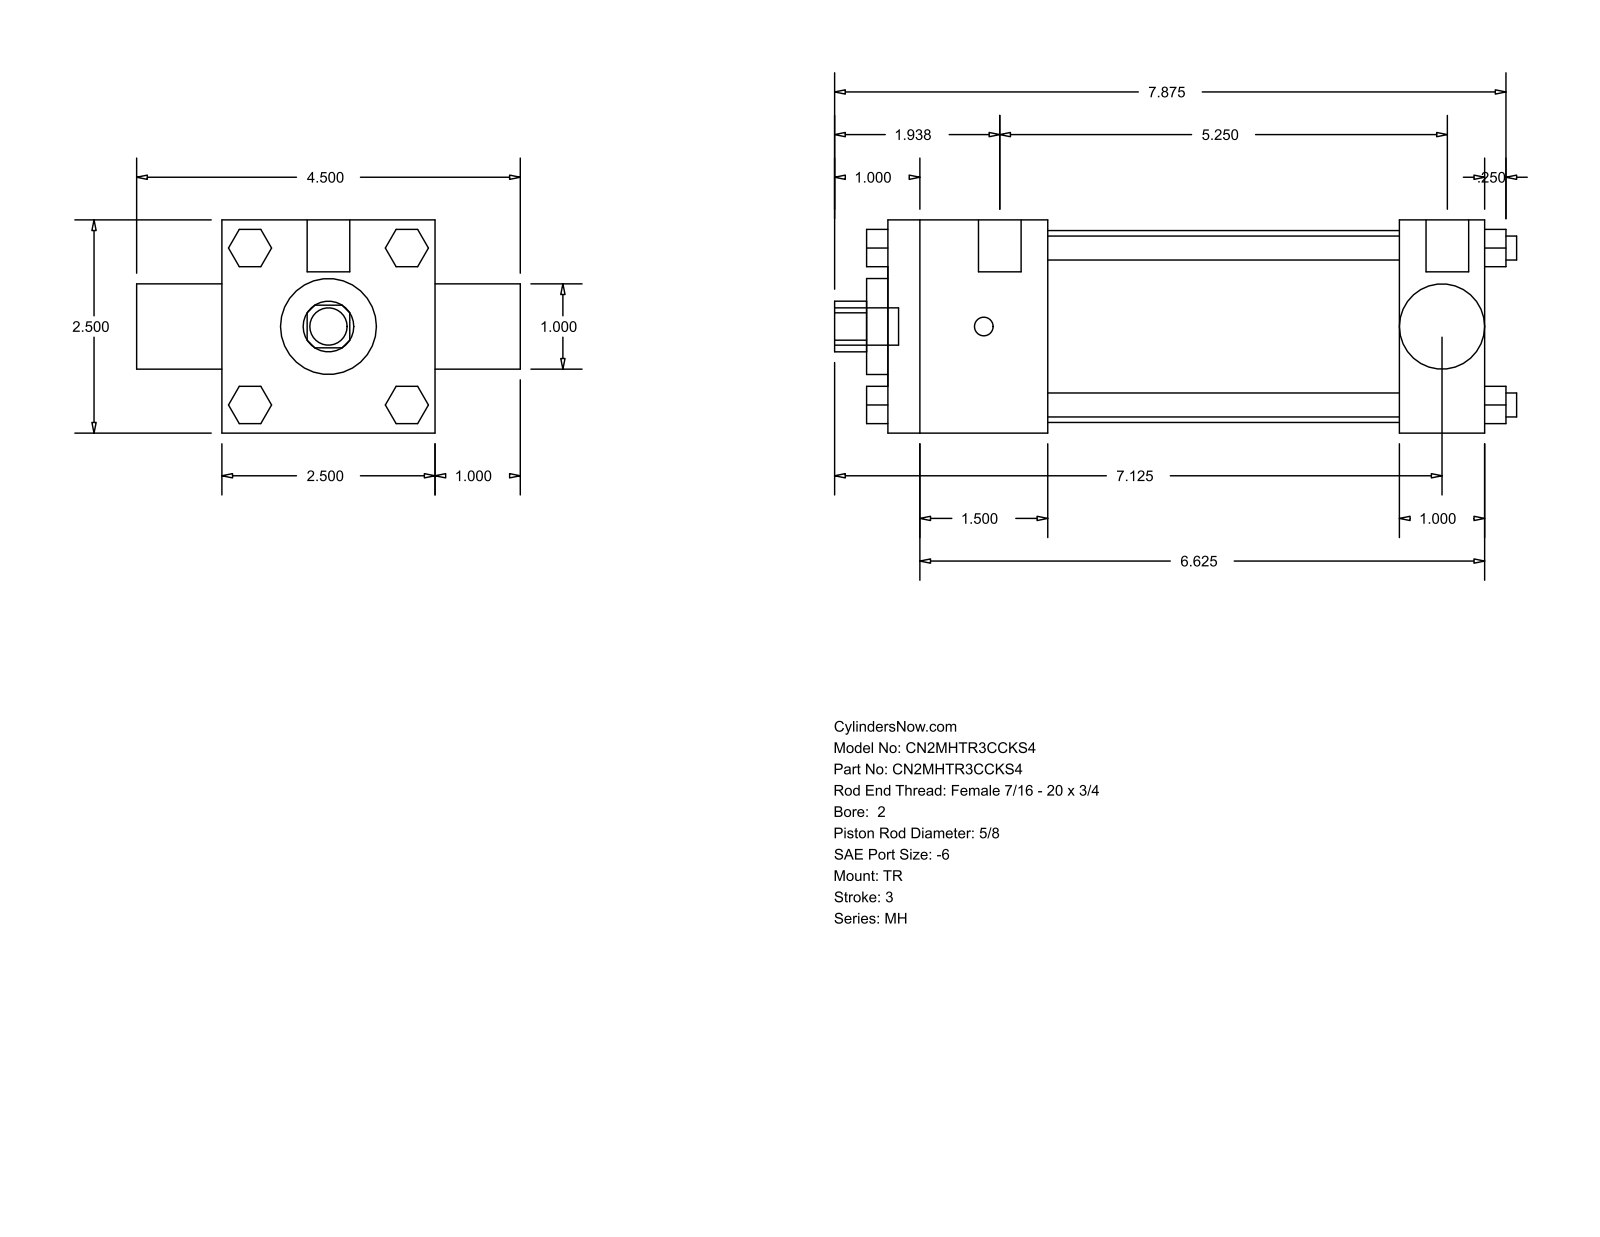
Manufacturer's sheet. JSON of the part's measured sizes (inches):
{"part_name": "MH_TR__0200_0.625", "step_written_by": "GSSL Pune (CONFIG_CONTROL_DESIGN)", "units": "inches", "bodies": {"solids": 0, "faces": 120, "planar": 92, "cylindrical": 28, "other": 0}, "overall_size": [8, 4.5, 2.5], "round_holes": [[0.625, 1], [0.998, 1], [1.125, 1], [2.25, 1]], "round_bosses_or_shafts": [[0.281, 4], [0.219, 3], [0.5, 2], [0.437, 1]], "partial_cylinders_radius": [[0.297, 1]], "face_to_face_distances": [2.5, 7, 1, 1.875, 6, 4.125, 5.125, 7.25, 0.25, 3.5]}
